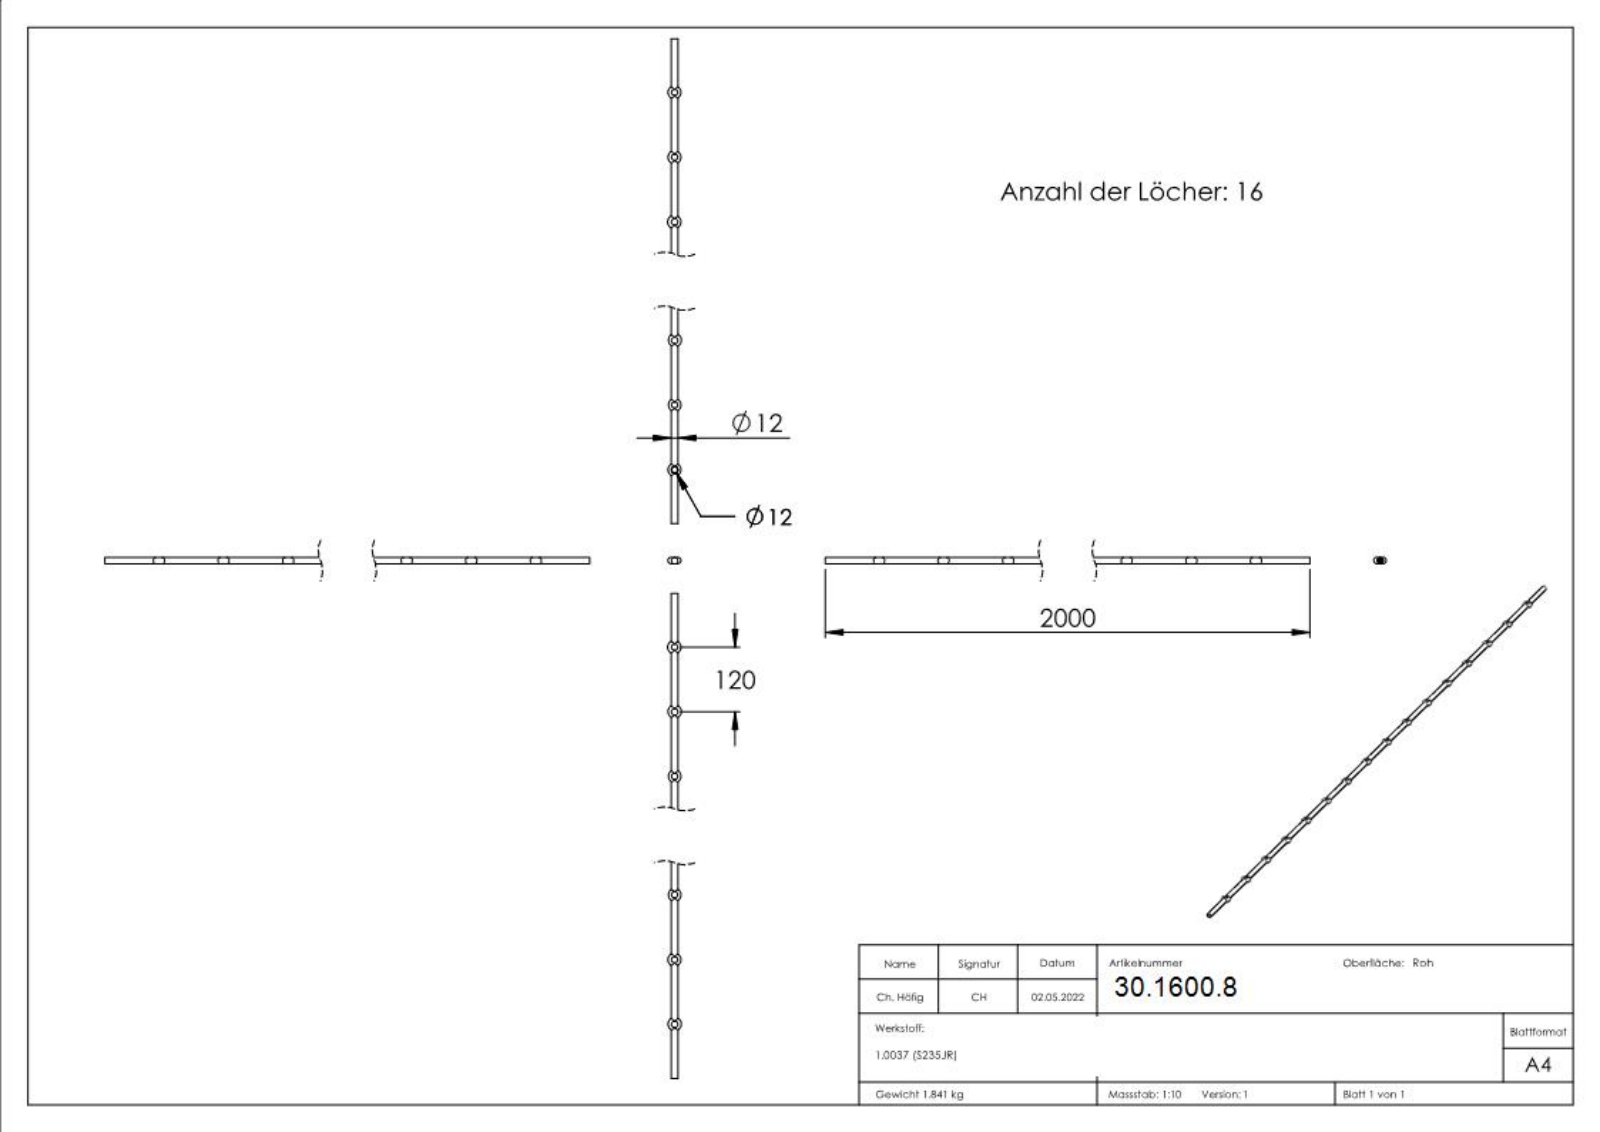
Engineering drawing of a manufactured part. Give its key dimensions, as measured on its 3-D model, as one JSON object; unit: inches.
{"part_name": "1447-I", "step_written_by": "SolidWorks 2018 (CONFIG_CONTROL_DESIGN)", "units": "inches", "bodies": {"solids": 1, "faces": 277, "planar": 144, "cylindrical": 33, "other": 100}, "overall_size": [78.74, 0.945, 0.472], "volume_in3": 14.41, "surface_area_in2": 133.2, "round_holes": [[0.472, 16]], "round_bosses_or_shafts": [[0.472, 1]], "face_to_face_distances": [78.74, 78.736, 0.035, 0.124, 0.08, 0.126, 0.177, 0.045, 0.139, 0.114], "hole_center_spacings": [4.724, 9.449, 14.173, 18.898, 23.622, 28.346, 33.071, 37.795]}
